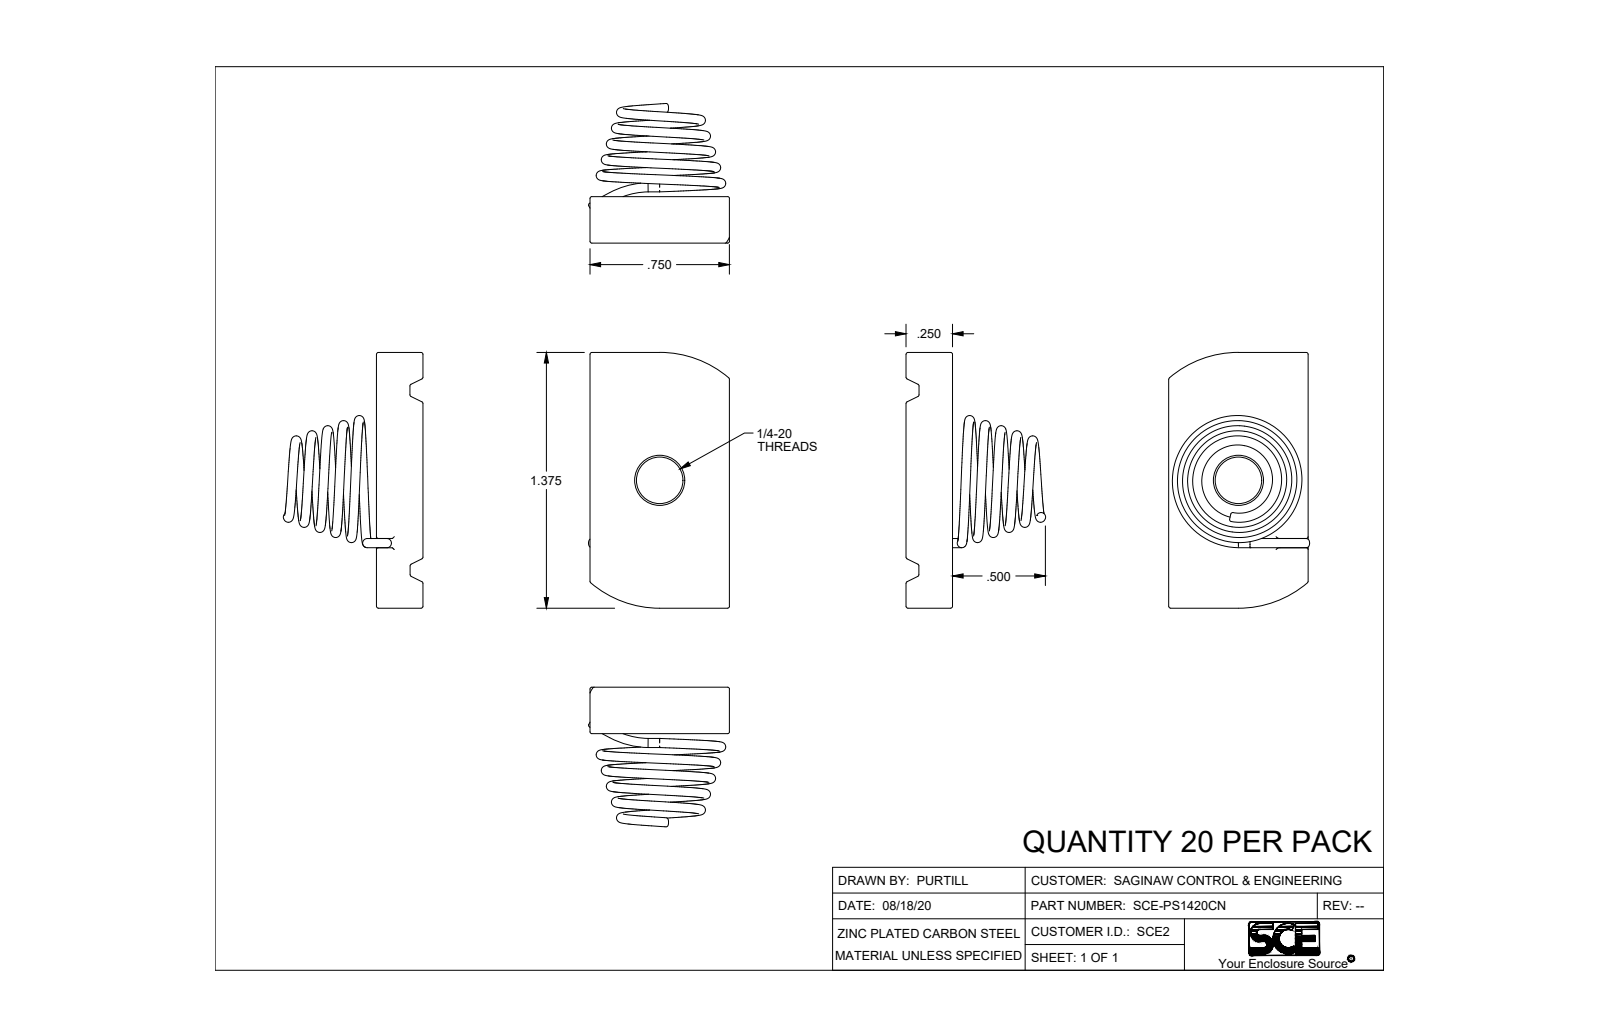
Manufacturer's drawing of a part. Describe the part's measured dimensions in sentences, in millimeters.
The part is named "SCE-PS1420CN". Its 3-D file was written by "SolidWorks 2019 (CONFIG_CONTROL_DESIGN)". It is 1 solid with 115 faces: 19 planar, 50 cylindrical and 46 other. Overall it measures 34.9 by 19.3 by 19.1 millimeters. Its volume is 4 000 cubic millimeters and its surface area 2 925 square millimeters. Round holes: 1 of diameter 6.4. Round bosses or shafts: 2 of diameter 1.2. Partial cylindrical surfaces (rounded edges, fillets, slot ends): 38 of radius 0.3, 2 of radius 14.5. The main face-to-face distances are 6.4, 19.1, 34.9, 4.6, 1.8, 4.6, 1.8, 9.5, 25.4, 8.3.
